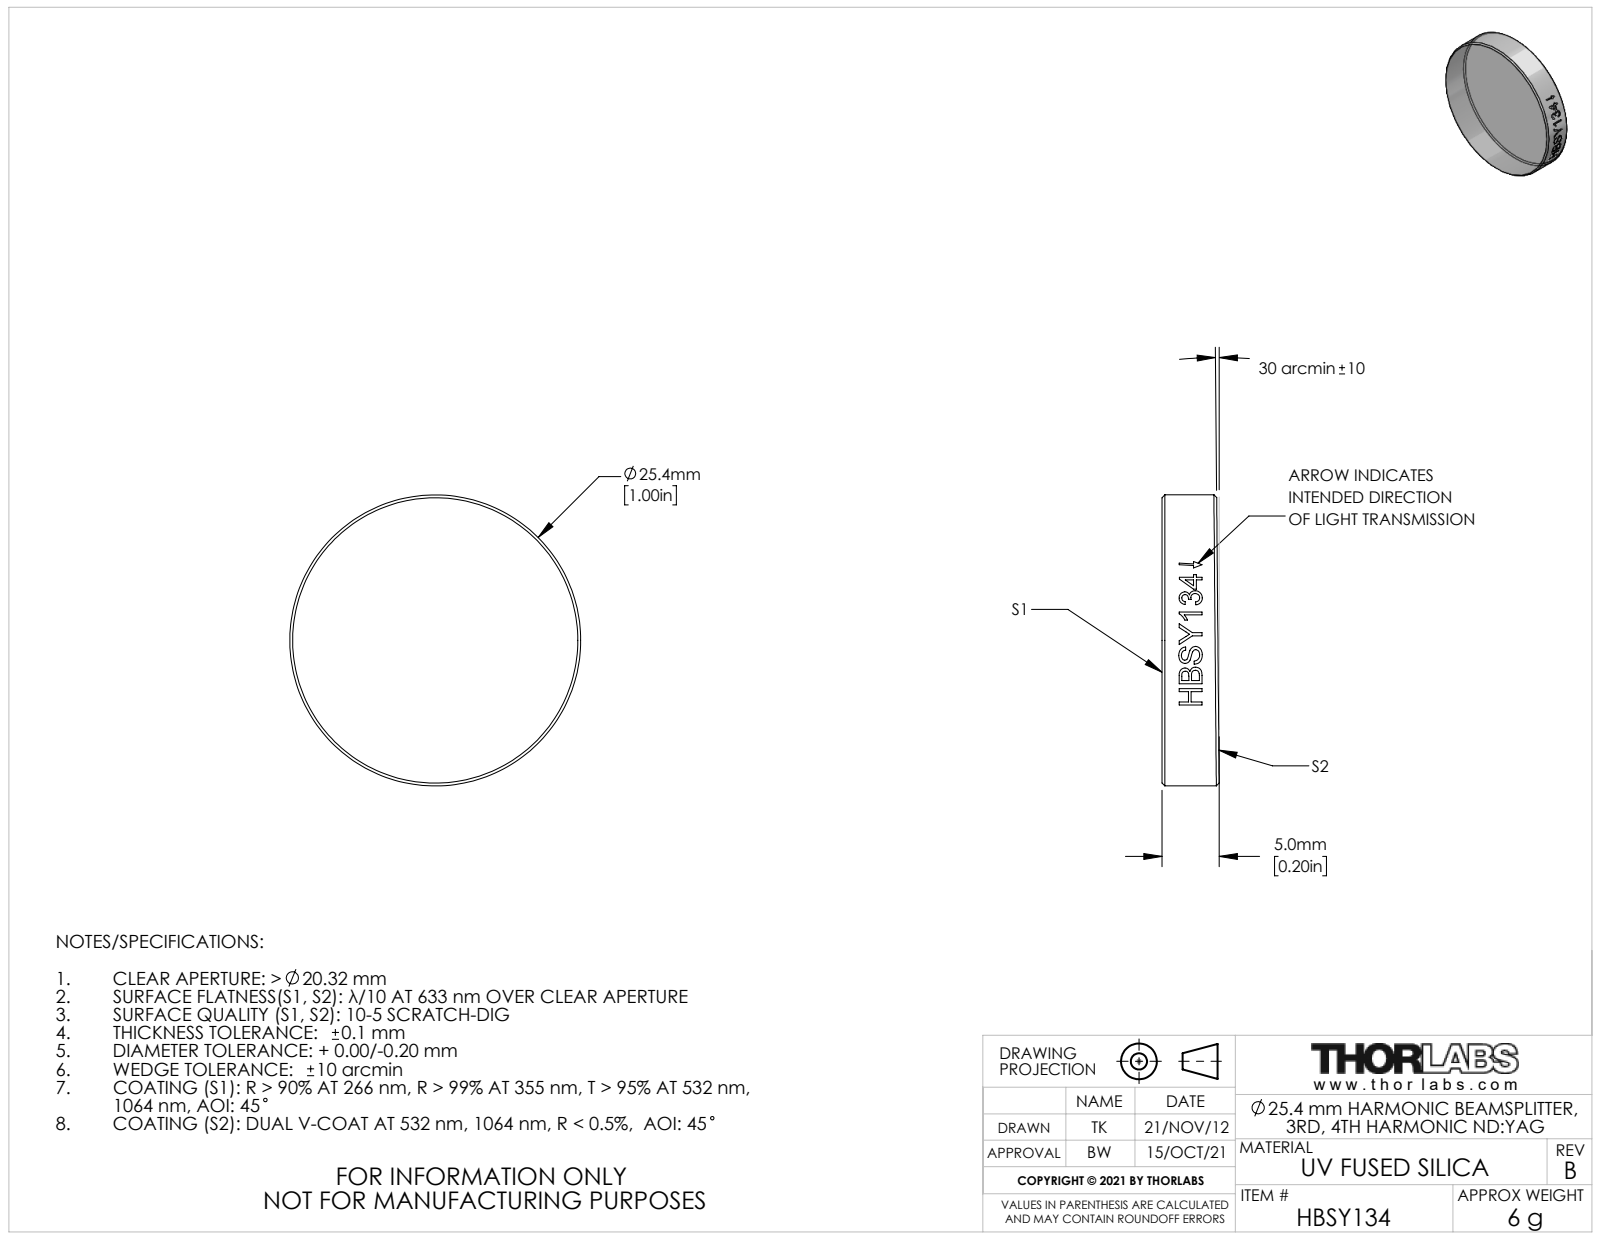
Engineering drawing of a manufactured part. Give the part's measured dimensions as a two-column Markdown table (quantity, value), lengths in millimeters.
| quantity | value |
| --- | --- |
| part name | TTN006425-E0W |
| STEP written by | SolidWorks 2012 (CONFIG_CONTROL_DESIGN) |
| units | millimeters |
| bodies | 1 solid, 19 faces (2 planar, 13 cylindrical, 4 other) |
| overall size | 25.4 × 25.4 × 5 |
| volume | 2 472 mm³ |
| surface area | 1 380 mm² |
| round bosses / shafts (diameter × count) | 25.4 × 1 |
